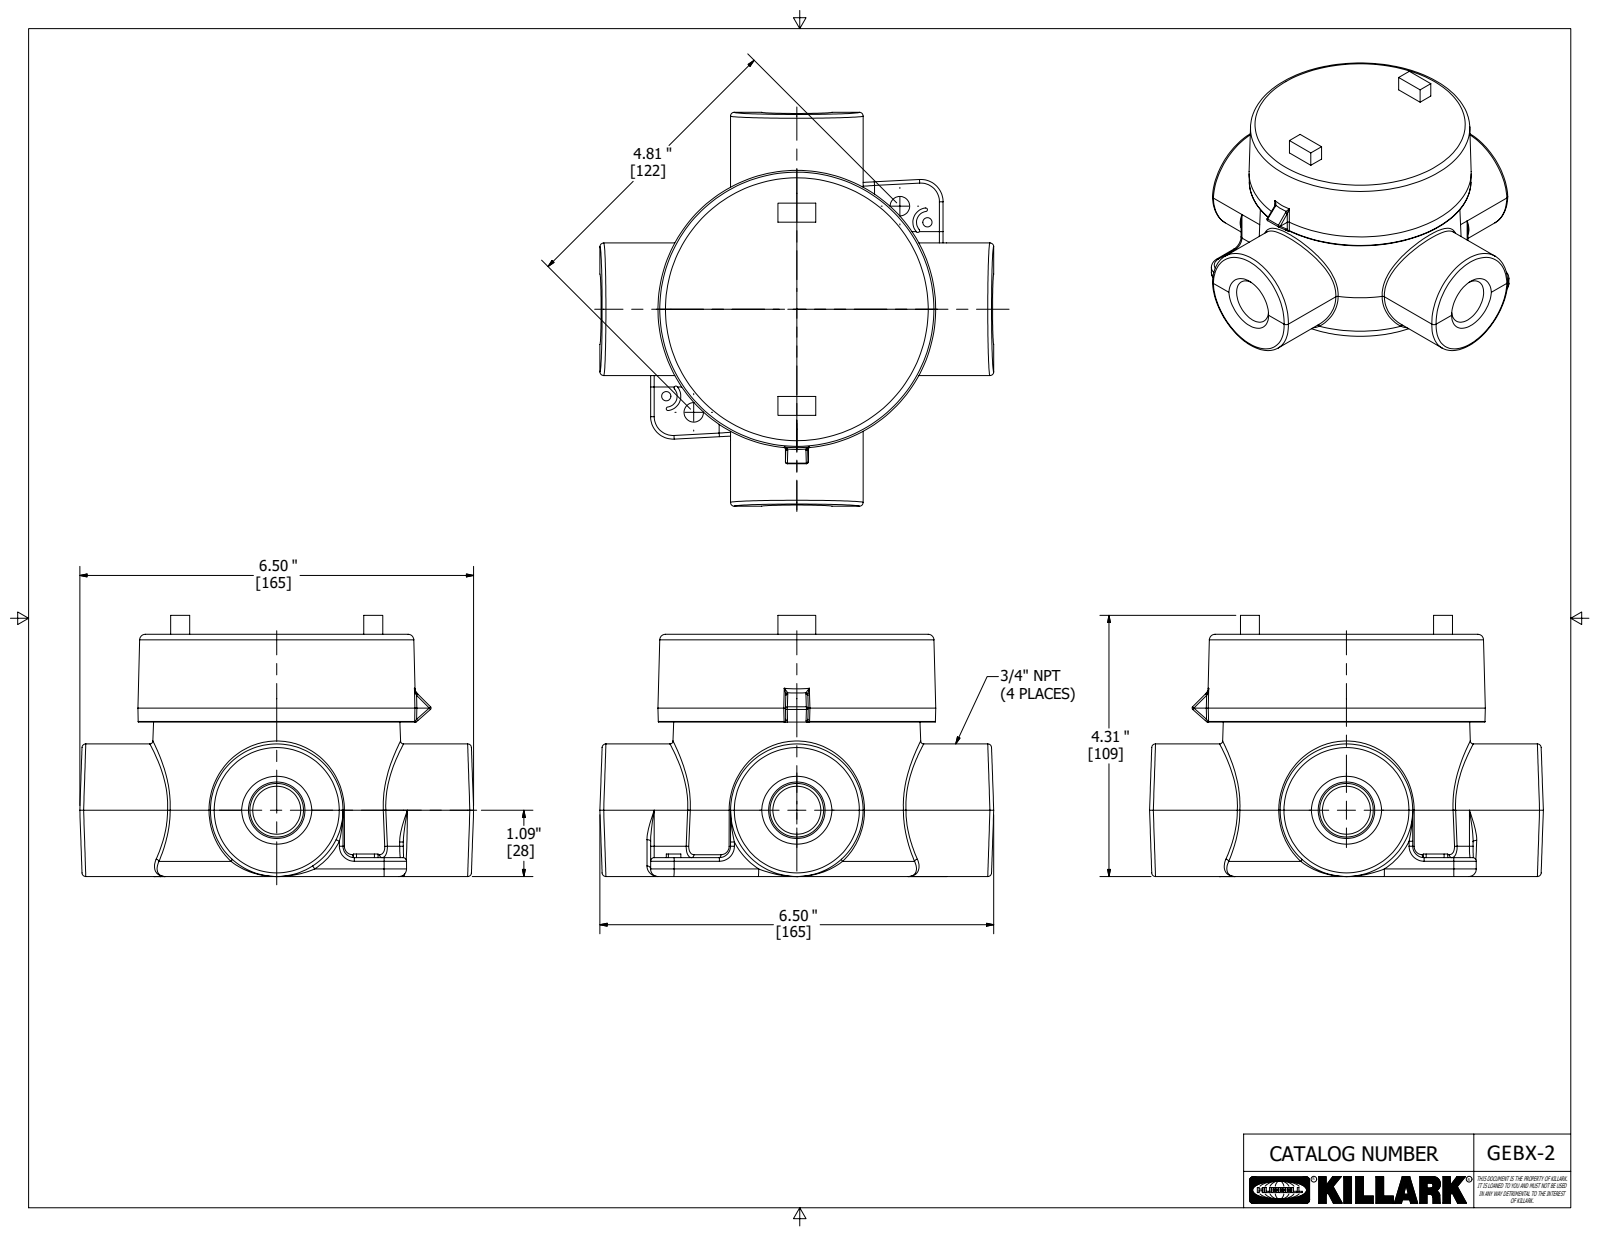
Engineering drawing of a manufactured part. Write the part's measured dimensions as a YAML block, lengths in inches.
part_name: "GEBX-2; 21151; 21147-override"
step_written_by: "Autodesk Inventor 2020 (AUTOMOTIVE_DESIGN)"
units: inches
bodies: {solids: 2, faces: 871, planar: 419, cylindrical: 99, other: 353}
overall_size: [6.5, 6.5, 4.31]
volume: 46.28
surface_area: 222
round_holes:
  - {diameter: 0.153, count: 2}
  - {diameter: 0.321, count: 2}
  - {diameter: 0.792, count: 2}
  - {diameter: 3.823, count: 1}
  - {diameter: 4.045, count: 1}
round_bosses_or_shafts:
  - {diameter: 2.188, count: 2}
partial_cylinders:
  - {radius: 0.06, count: 35}
  - {radius: 0.03, count: 14}
  - {radius: 0.125, count: 4}
  - {radius: 0.187, count: 4}
  - {radius: 0.031, count: 3}
  - {radius: 0.18, count: 2}
  - {radius: 0.24, count: 2}
  - {radius: 0.37, count: 2}
face_to_face_distances: [3.998, 3.56, 0.438, 2.549, 1.011, 1.449, 3.5, 0.38, 2.169, 3.18]
hole_center_spacings: [0.527, 4.97, 2.406, 2.406, 2.589, 2.589, 4.812, 5.178]
